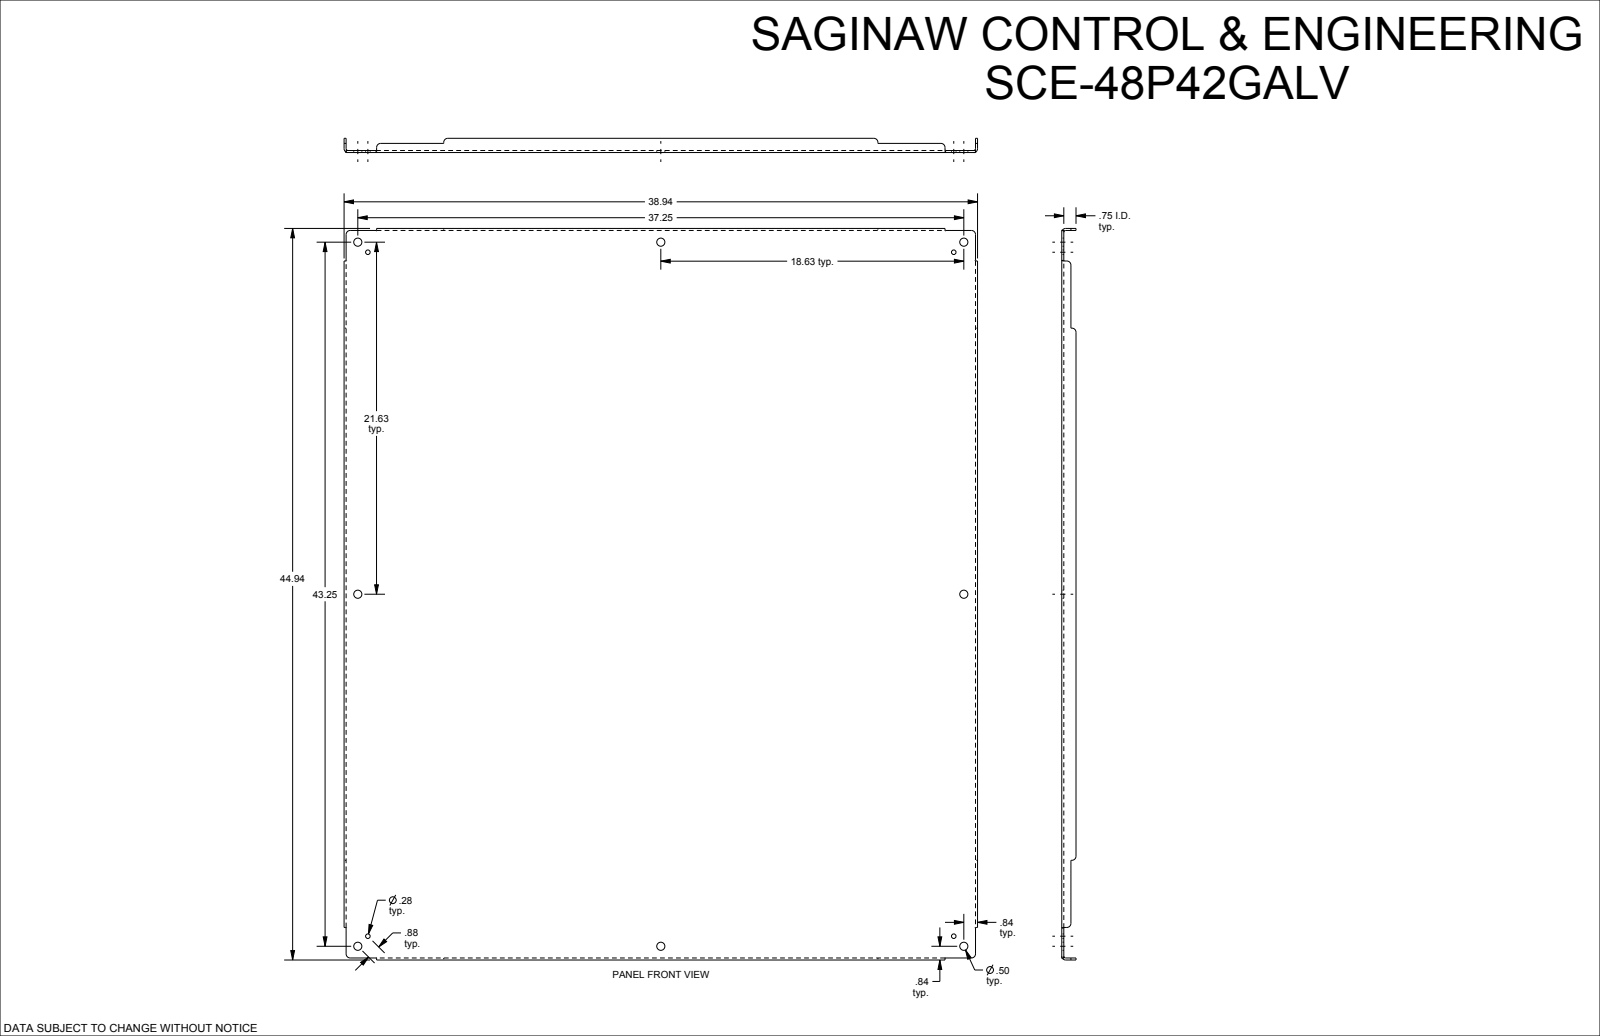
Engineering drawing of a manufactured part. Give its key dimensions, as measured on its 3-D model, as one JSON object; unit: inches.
{"part_name": "SCE-48P42GALV", "step_written_by": "SolidWorks 2019 (CONFIG_CONTROL_DESIGN)", "units": "inches", "bodies": {"solids": 1, "faces": 110, "planar": 46, "cylindrical": 40, "other": 24}, "overall_size": [44.938, 38.938, 0.875], "volume_in3": 229.7, "surface_area_in2": 3699, "round_holes": [[0.5, 8], [0.281, 4]], "partial_cylinders_radius": [[0.25, 12], [0.112, 4], [0.237, 4]], "face_to_face_distances": [0.125, 0.125, 38.813, 44.813, 38.687, 38.938, 44.687, 44.938, 0.75, 0.875], "hole_center_spacings": [0.875, 18.017, 18.625, 21.015, 21.625, 28.54, 36.636, 42.227]}
